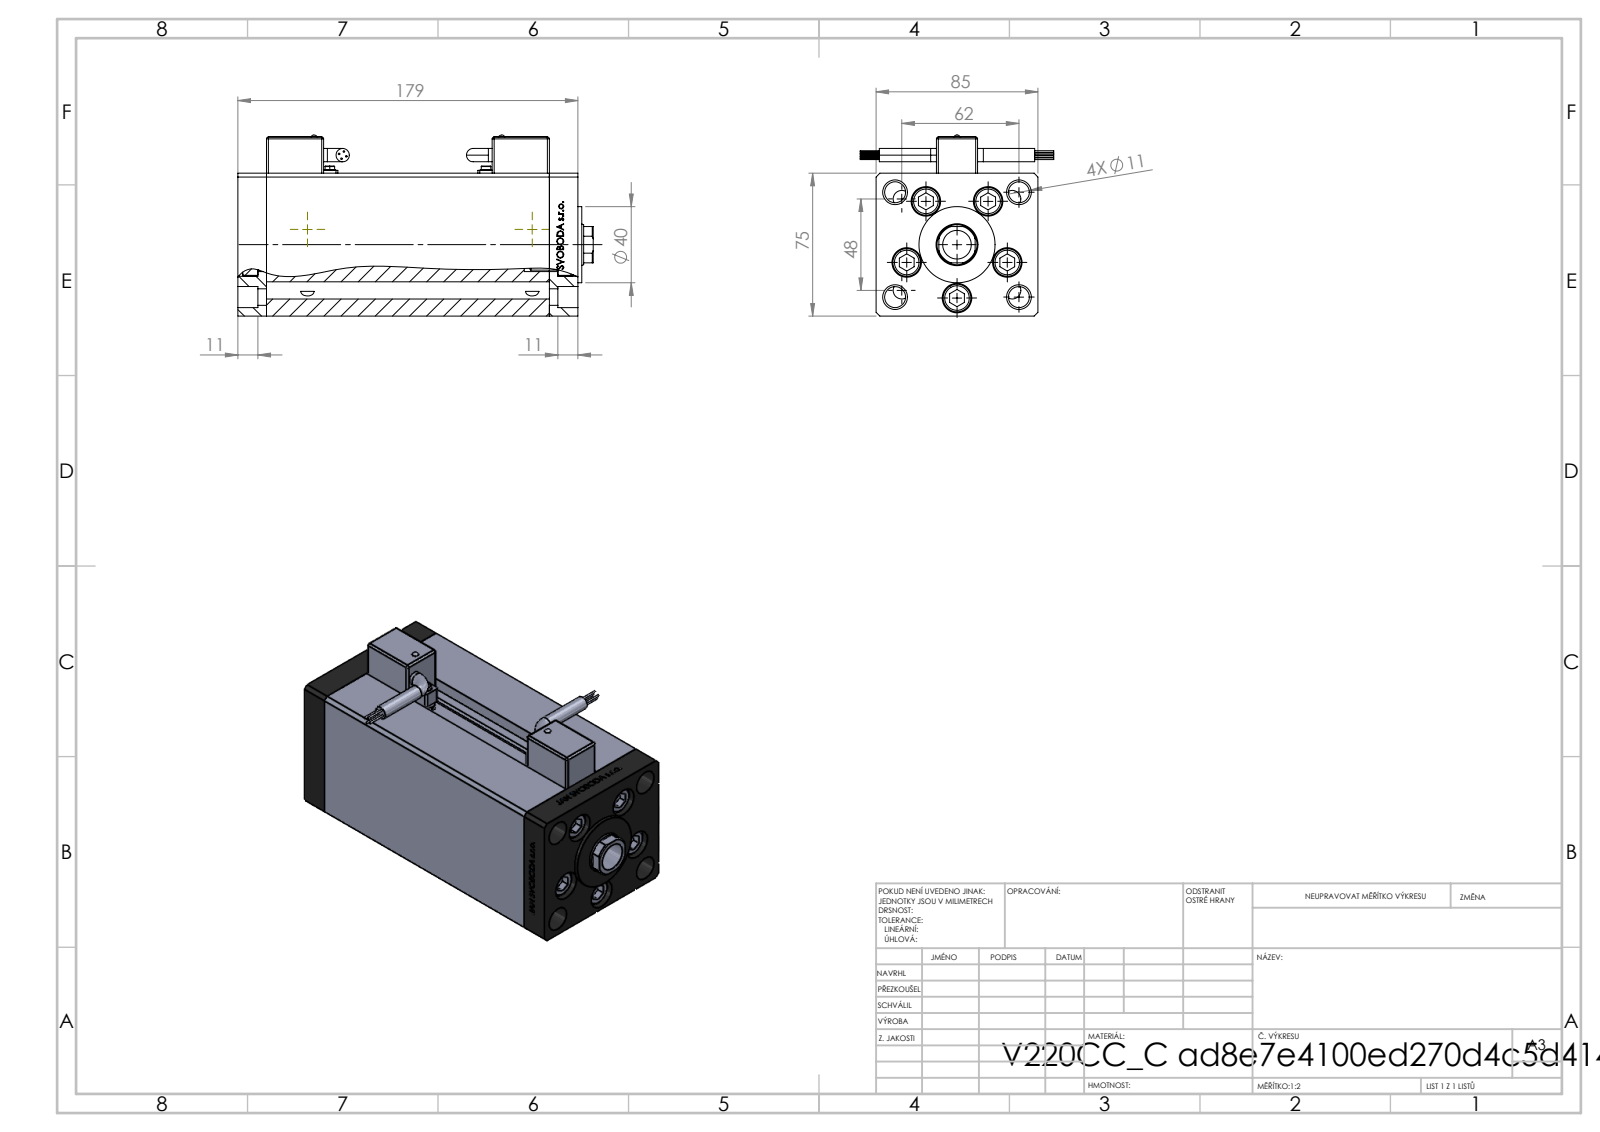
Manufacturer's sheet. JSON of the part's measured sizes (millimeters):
{"part_name": "ALLEN BOLT; V220C_C CAST PRO VYSUNUTI; V220C FRONT; V220C_C MIDDLE (+2 more)", "step_written_by": "SolidWorks 2019 (CONFIG_CONTROL_DESIGN)", "units": "millimeters", "bodies": {"solids": 16, "faces": 1399, "planar": 630, "cylindrical": 265, "other": 504}, "overall_size": [186.5, 101.6, 95.1], "volume_mm3": 997733, "surface_area_mm2": 188374, "round_holes": [[11, 9], [15.5, 5], [2, 4], [9, 4], [13, 4], [13.16, 4], [3.6, 2], [5, 2], [7, 2], [15, 1], [22, 1]], "round_bosses_or_shafts": [[0.85, 8], [14.5, 5], [8, 5], [7, 4], [6, 2], [3.5, 2], [2.5, 2], [40, 1]], "partial_cylinders_radius": [[1, 24], [4, 4], [0.93, 2], [10.5, 1]], "face_to_face_distances": [85, 75, 148.5, 15, 163.5, 10.5, 178.5, 68.5, 6.5, 31.7], "hole_center_spacings": [28, 4.95, 37.64, 42.57, 51.62, 61.6, 80.22, 8.25]}
